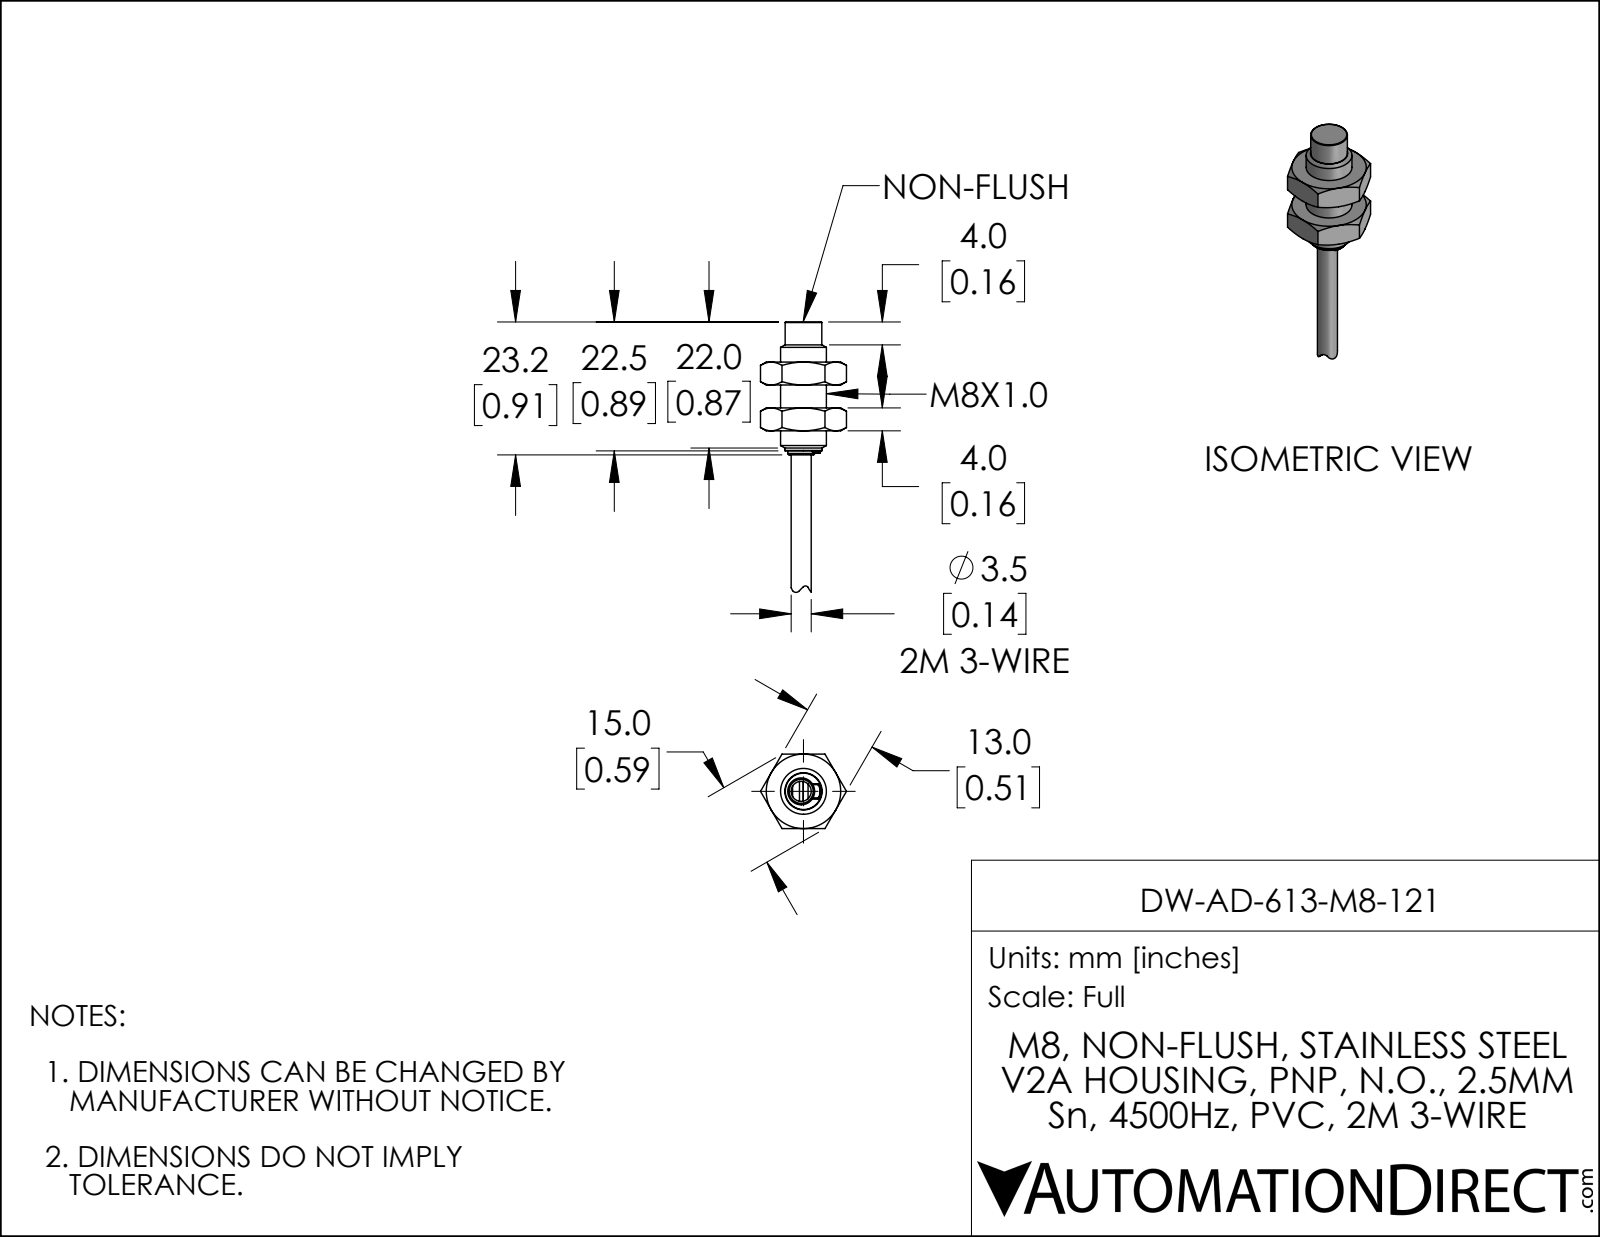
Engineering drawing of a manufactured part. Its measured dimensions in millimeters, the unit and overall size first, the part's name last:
Units: millimetres
Overall size (bounding box): 47.2 × 15 × 13
Round bosses / shafts (diameter × count): ⌀8 ×1, ⌀6.5 ×1, ⌀6.4 ×1, ⌀4.7 ×1, ⌀3.5 ×1
Partial cylindrical surfaces — rounded edges, fillets, slot ends (radius × count): R0.3 ×2, R0.6 ×1, R0.8 ×1, R2.9 ×1, R3 ×1, R4.5 ×1, R6 ×1
Main face-to-face distances: 4, 8, 13, 12, 7, 11, 15, 19, 22.5, 15.5
Volume: 2 050 mm³ · Surface area: 1 413 mm²
Bodies: 1 solid, 78 faces (23 planar, 19 cylindrical, 36 other)
Part name (STEP PRODUCT): DW-AD-613-M8-121
STEP written by: SolidWorks 2019 (AUTOMOTIVE_DESIGN)
